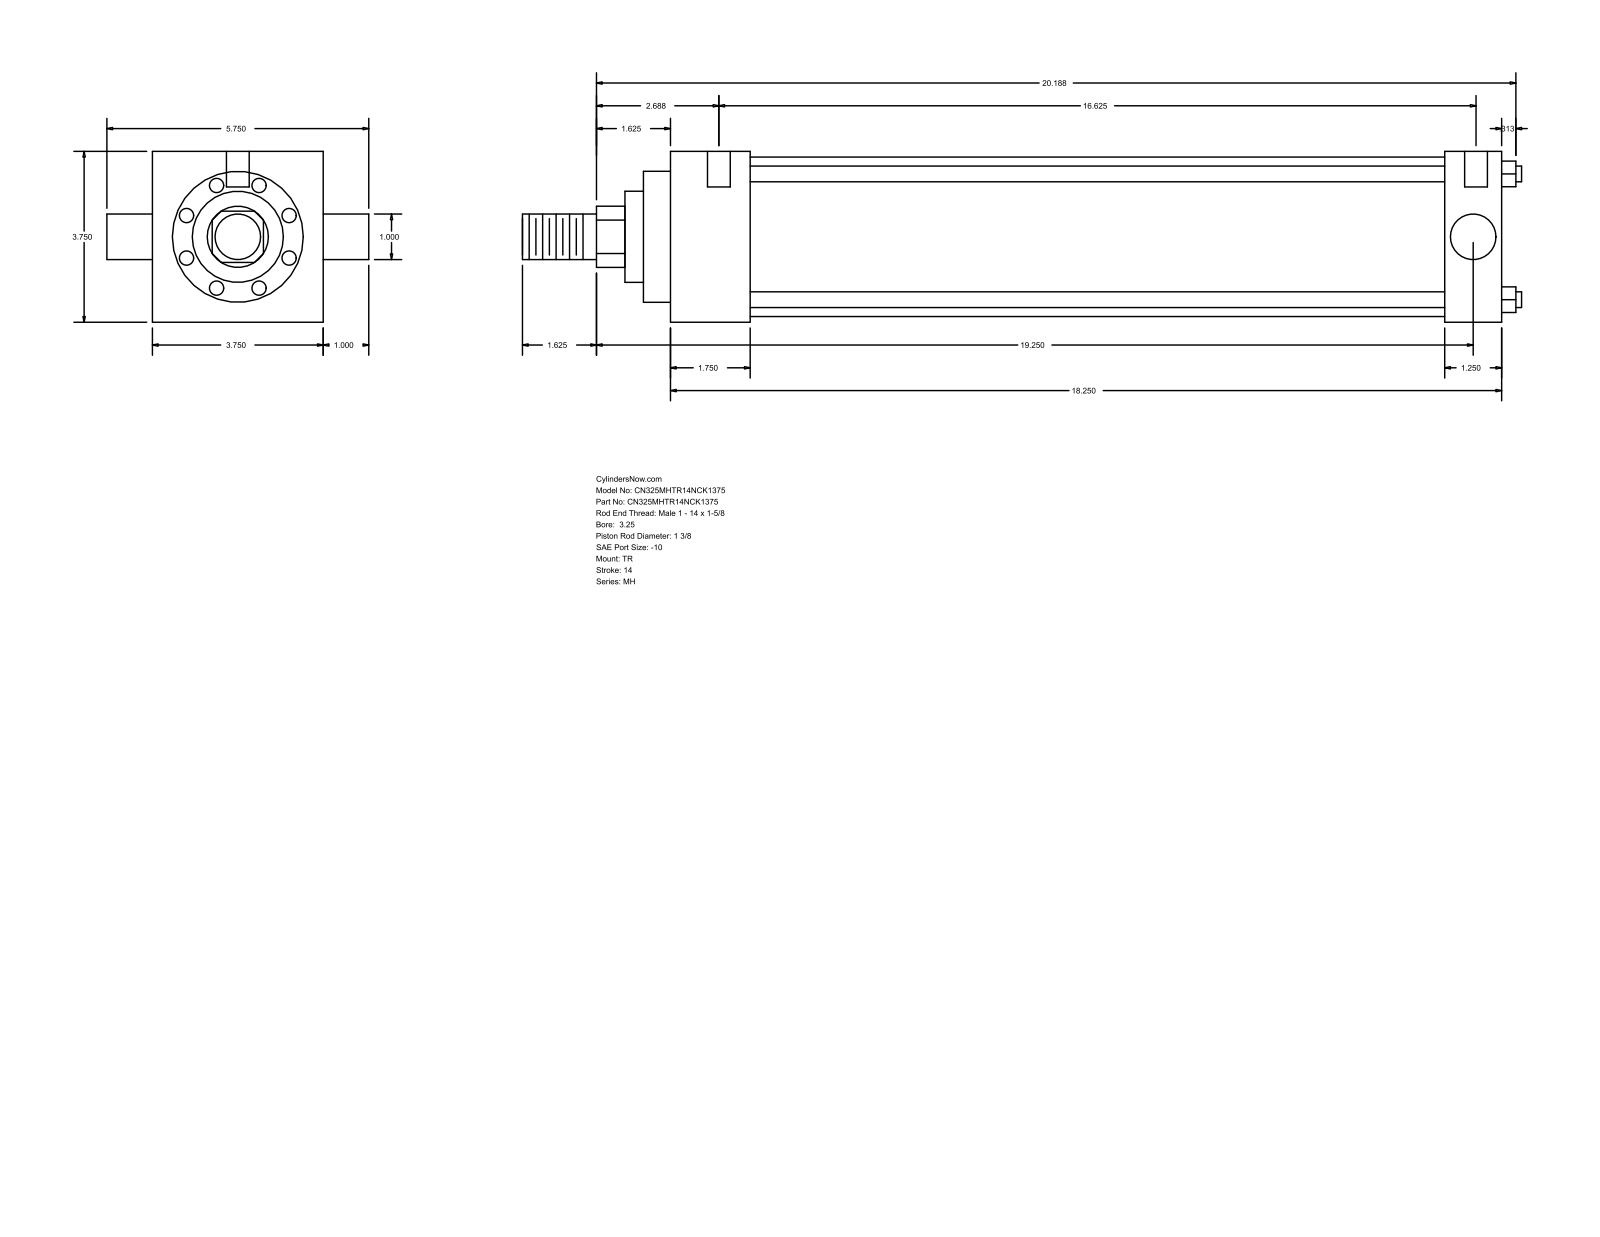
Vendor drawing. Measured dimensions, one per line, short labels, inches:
name: MH_TR__0325_1.375
written by: GSSL Pune (CONFIG_CONTROL_DESIGN)
unit: in
bodies: 0 solids, 86 faces (61 planar, 25 cylindrical, 0 other)
size: 21.937 × 5.75 × 3.75
holes: 3× ⌀0.219, 2× ⌀0.5
bosses: 4× ⌀0.345, 2× ⌀1, 1× ⌀3.5, 1× ⌀2.875, 1× ⌀2, 1× ⌀1.375
rounds: 1× R0.672
face distances: 3.75, 18.25, 1.75, 17, 15.25, 16.5, 1.25, 0.594, 2.344, 17.594
hole spacings: 0.063, 0.187, 16.625, 16.688, 16.813, 16.875
